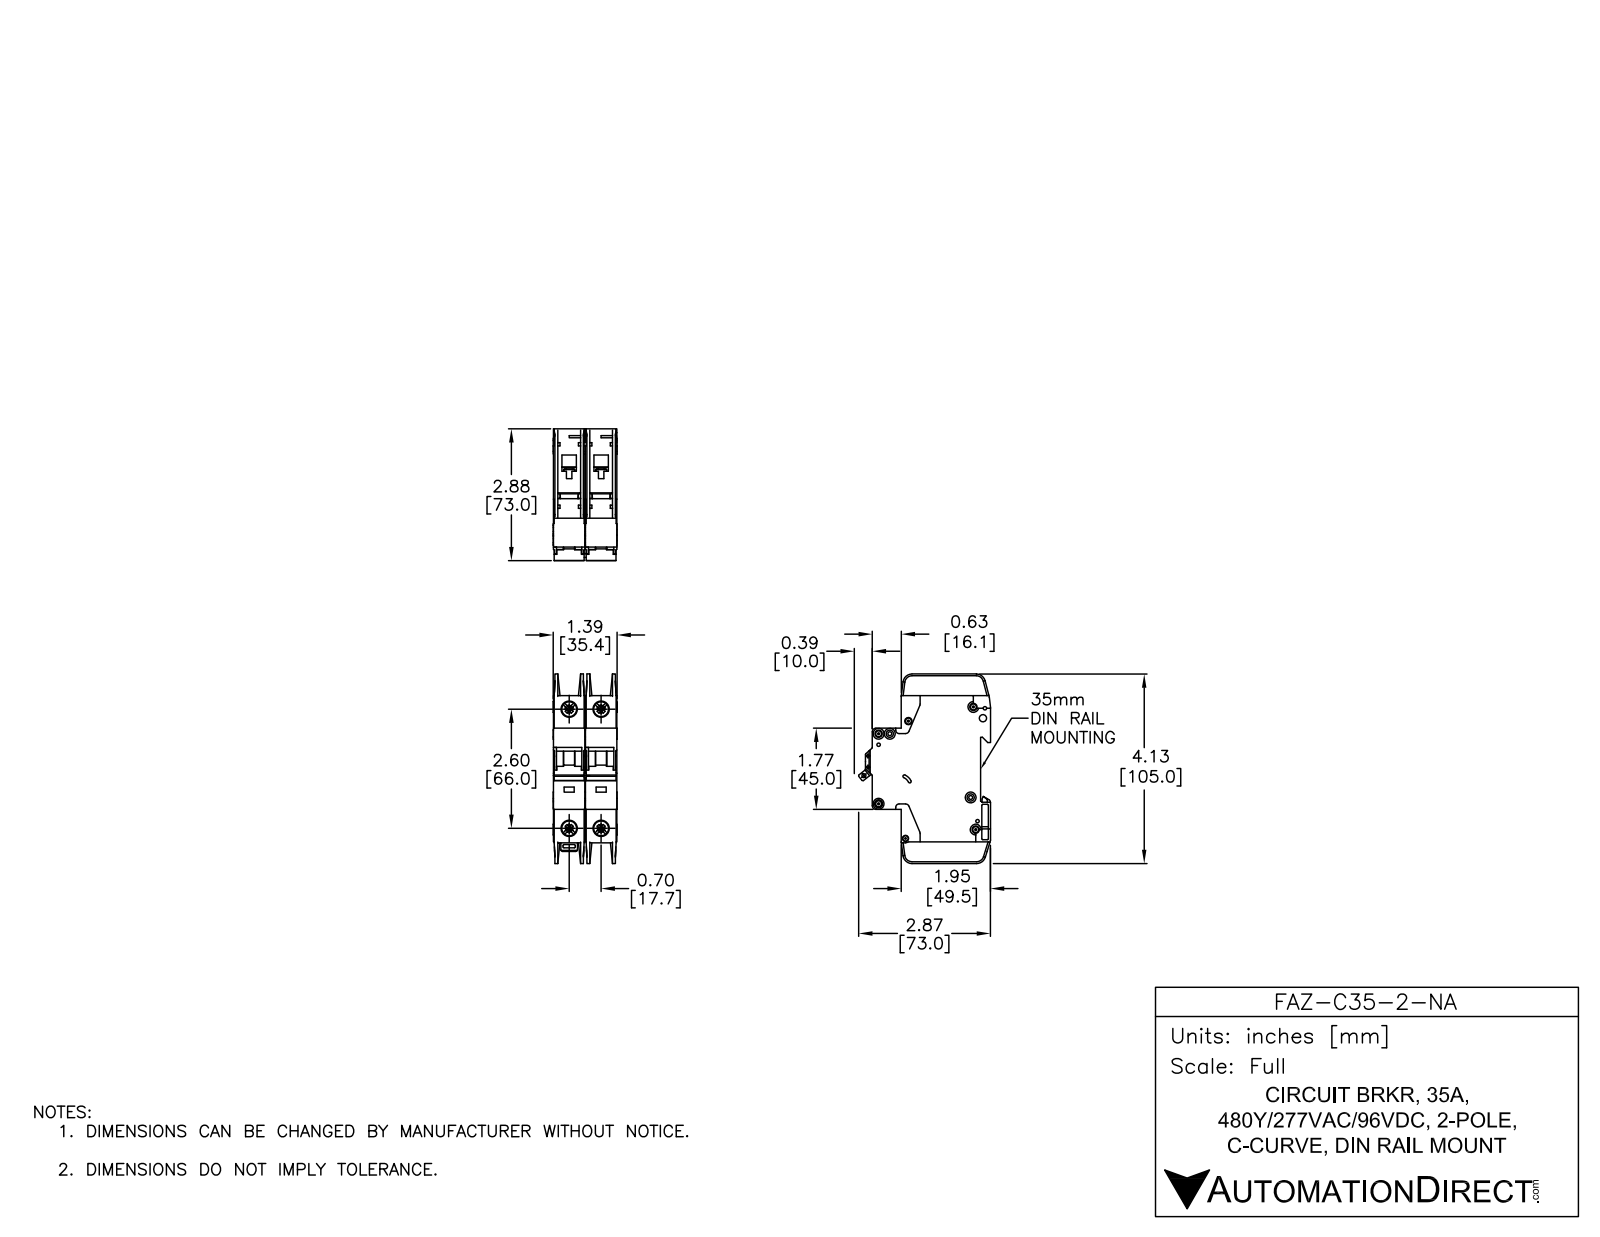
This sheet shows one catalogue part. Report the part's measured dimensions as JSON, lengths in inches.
{"part_name": "FAZ-C35-2-NA", "step_written_by": "SolidWorks 2014 (AUTOMOTIVE_DESIGN)", "units": "inches", "bodies": {"solids": 6, "faces": 1568, "planar": 818, "cylindrical": 526, "other": 224}, "overall_size": [4.134, 2.876, 1.394], "volume_in3": 9.482, "surface_area_in2": 76.69, "round_holes": [[0.142, 7], [0.281, 4], [0.323, 4], [0.043, 2], [0.059, 2], [0.157, 2], [0.075, 1], [0.085, 1], [0.087, 1], [0.1, 1], [0.13, 1], [0.134, 1]], "round_bosses_or_shafts": [[0.236, 7], [0.098, 2]], "partial_cylinders_radius": [[0.01, 47], [0.02, 24], [0.039, 18], [0.079, 12], [0.197, 5], [0.071, 4], [0.157, 4], [0.008, 2]], "face_to_face_distances": [0.697, 0.689, 0.028, 0.593, 0.096, 0.069, 0.62, 0.524, 1.386, 0.669], "hole_center_spacings": [0.244, 0.697, 2.598, 2.69, 0.204, 0.24, 0.322, 0.337]}
